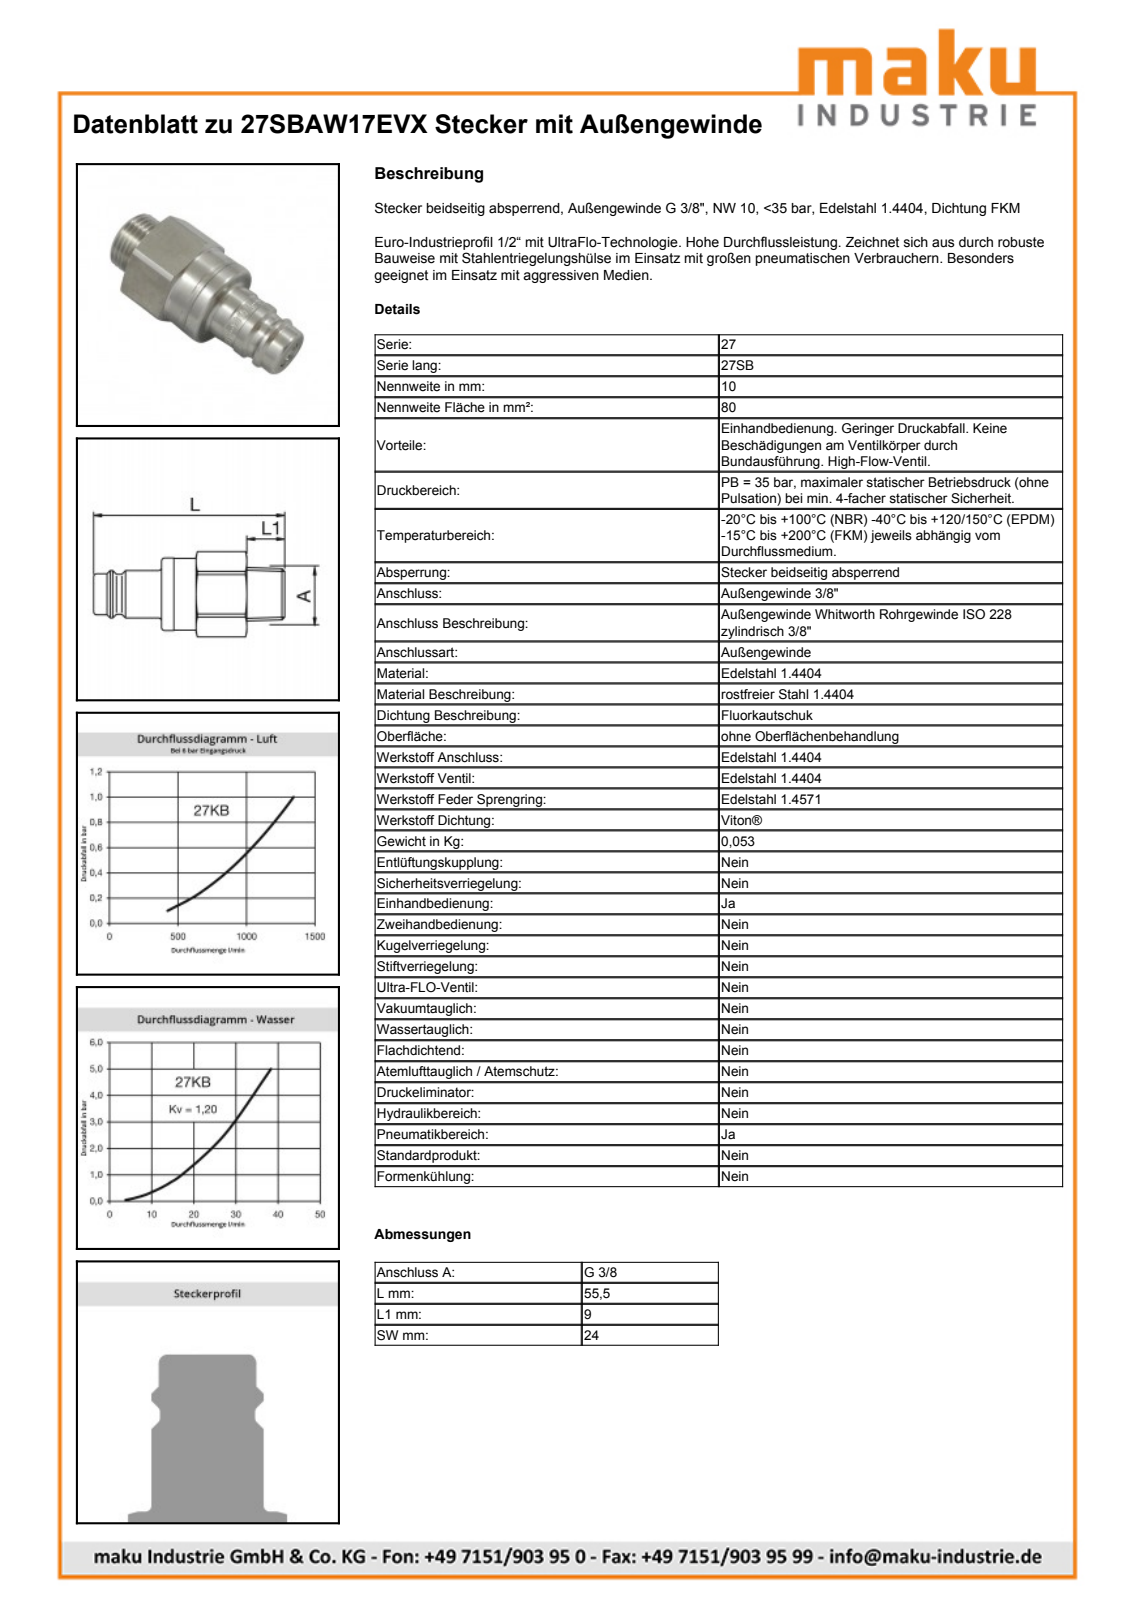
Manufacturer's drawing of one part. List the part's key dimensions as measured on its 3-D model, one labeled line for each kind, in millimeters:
Part name (STEP PRODUCT): D110590
STEP written by: Autodesk Inventor 2013 (AUTOMOTIVE_DESIGN)
Units: millimetres
Bodies: 1 solid, 59 faces (14 planar, 18 cylindrical, 27 other)
Overall size (bounding box): 55.4 × 26.69 × 26.05
Volume: 16 639 mm³ · Surface area: 5 073 mm²
Round holes (diameter × count): ⌀19 ×1, ⌀20.3 ×1
Round bosses / shafts (diameter × count): ⌀23 ×1, ⌀22.8 ×1, ⌀18.84 ×1, ⌀18.5 ×1, ⌀16.66 ×1, ⌀15 ×1, ⌀13 ×1, ⌀12.65 ×1
Partial cylindrical surfaces — rounded edges, fillets, slot ends (radius × count): R13.53 ×1
Main face-to-face distances: 24, 9, 24.9, 33.9, 21.5, 46.4, 55.4, 25.4, 3.9, 21
